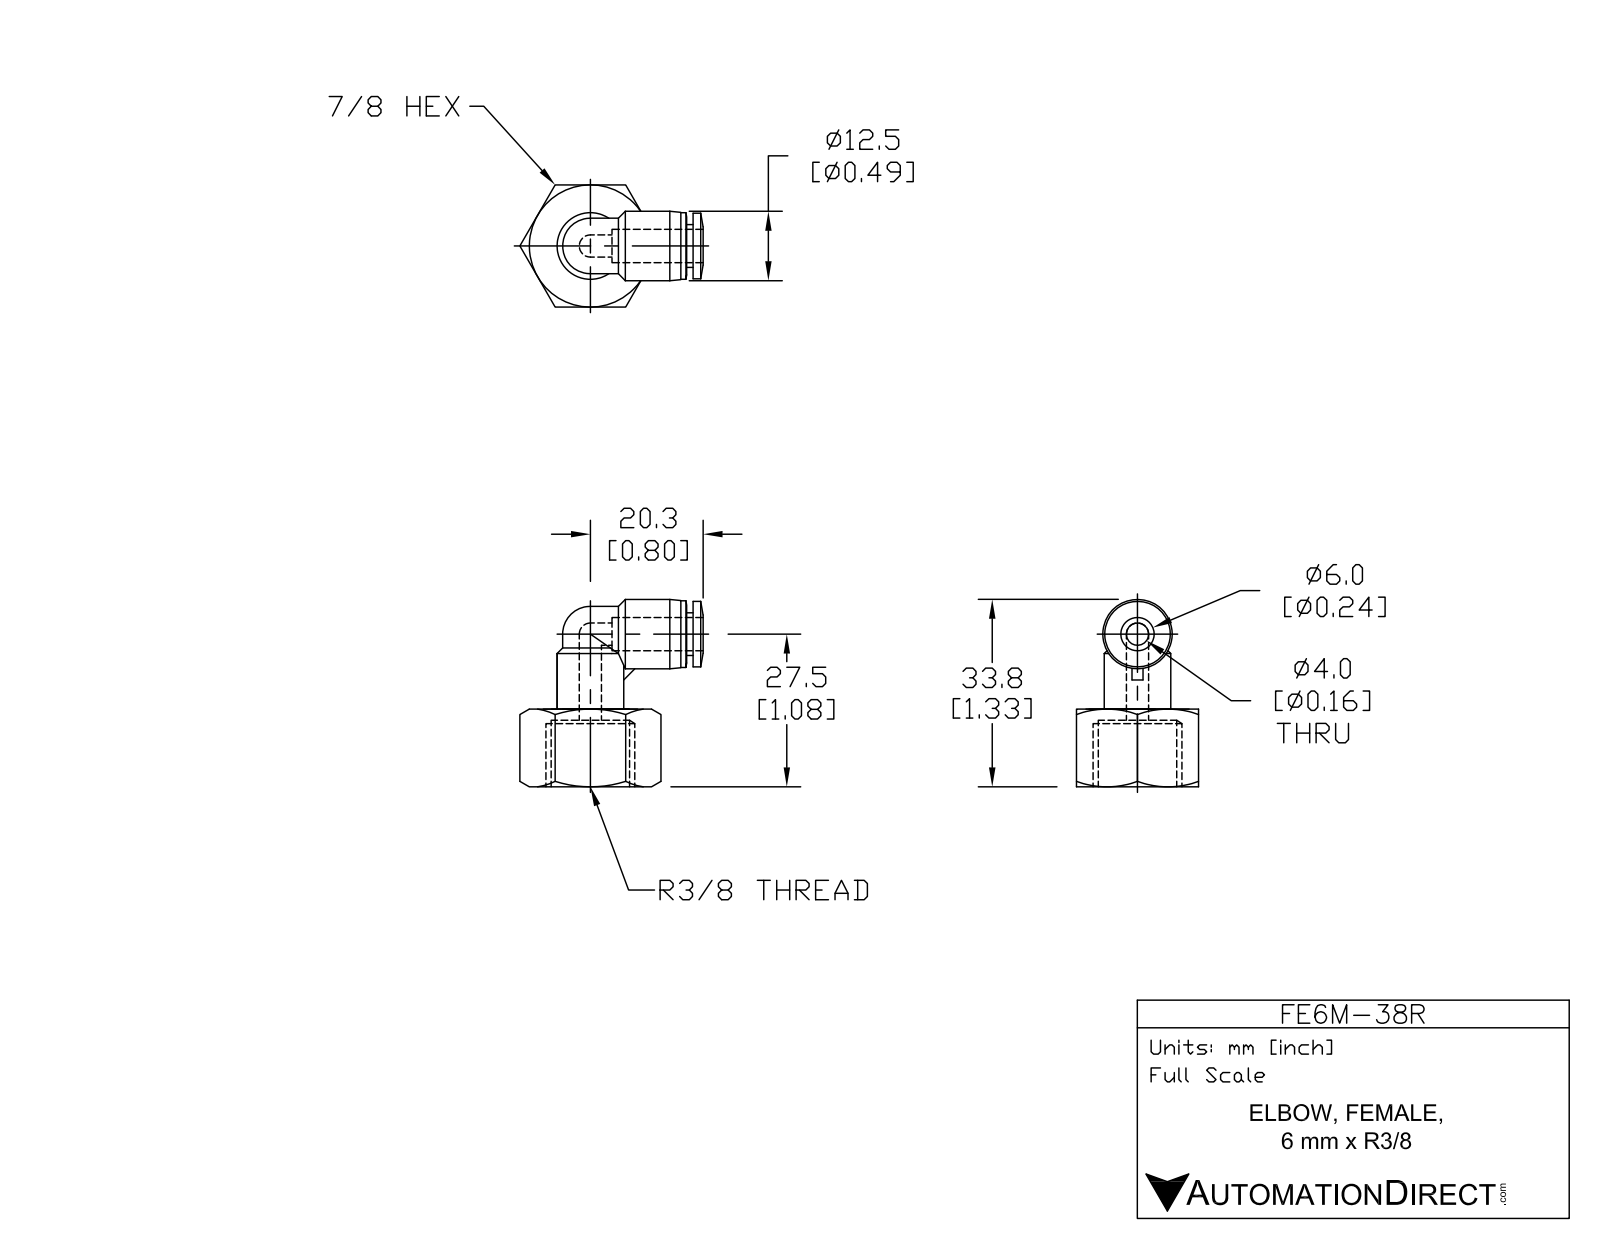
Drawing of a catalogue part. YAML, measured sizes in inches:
part_name: "FE6M-38R"
step_written_by: "SolidWorks 2015 (AUTOMOTIVE_DESIGN)"
units: inches
bodies: {solids: 1, faces: 67, planar: 17, cylindrical: 19, other: 31}
overall_size: [1.329, 1.299, 0.866]
volume: 0.37
surface_area: 6.694
round_holes:
  - {diameter: 0.157, count: 2}
  - {diameter: 0.248, count: 1}
round_bosses_or_shafts:
  - {diameter: 0.472, count: 2}
  - {diameter: 0.492, count: 1}
  - {diameter: 0.465, count: 1}
  - {diameter: 0.303, count: 1}
partial_cylinders:
  - {radius: 0.197, count: 2}
face_to_face_distances: [0.866, 0.079, 0.472, 0.551, 0.045, 0.53, 0.575, 0.394, 0.646, 0.116]
